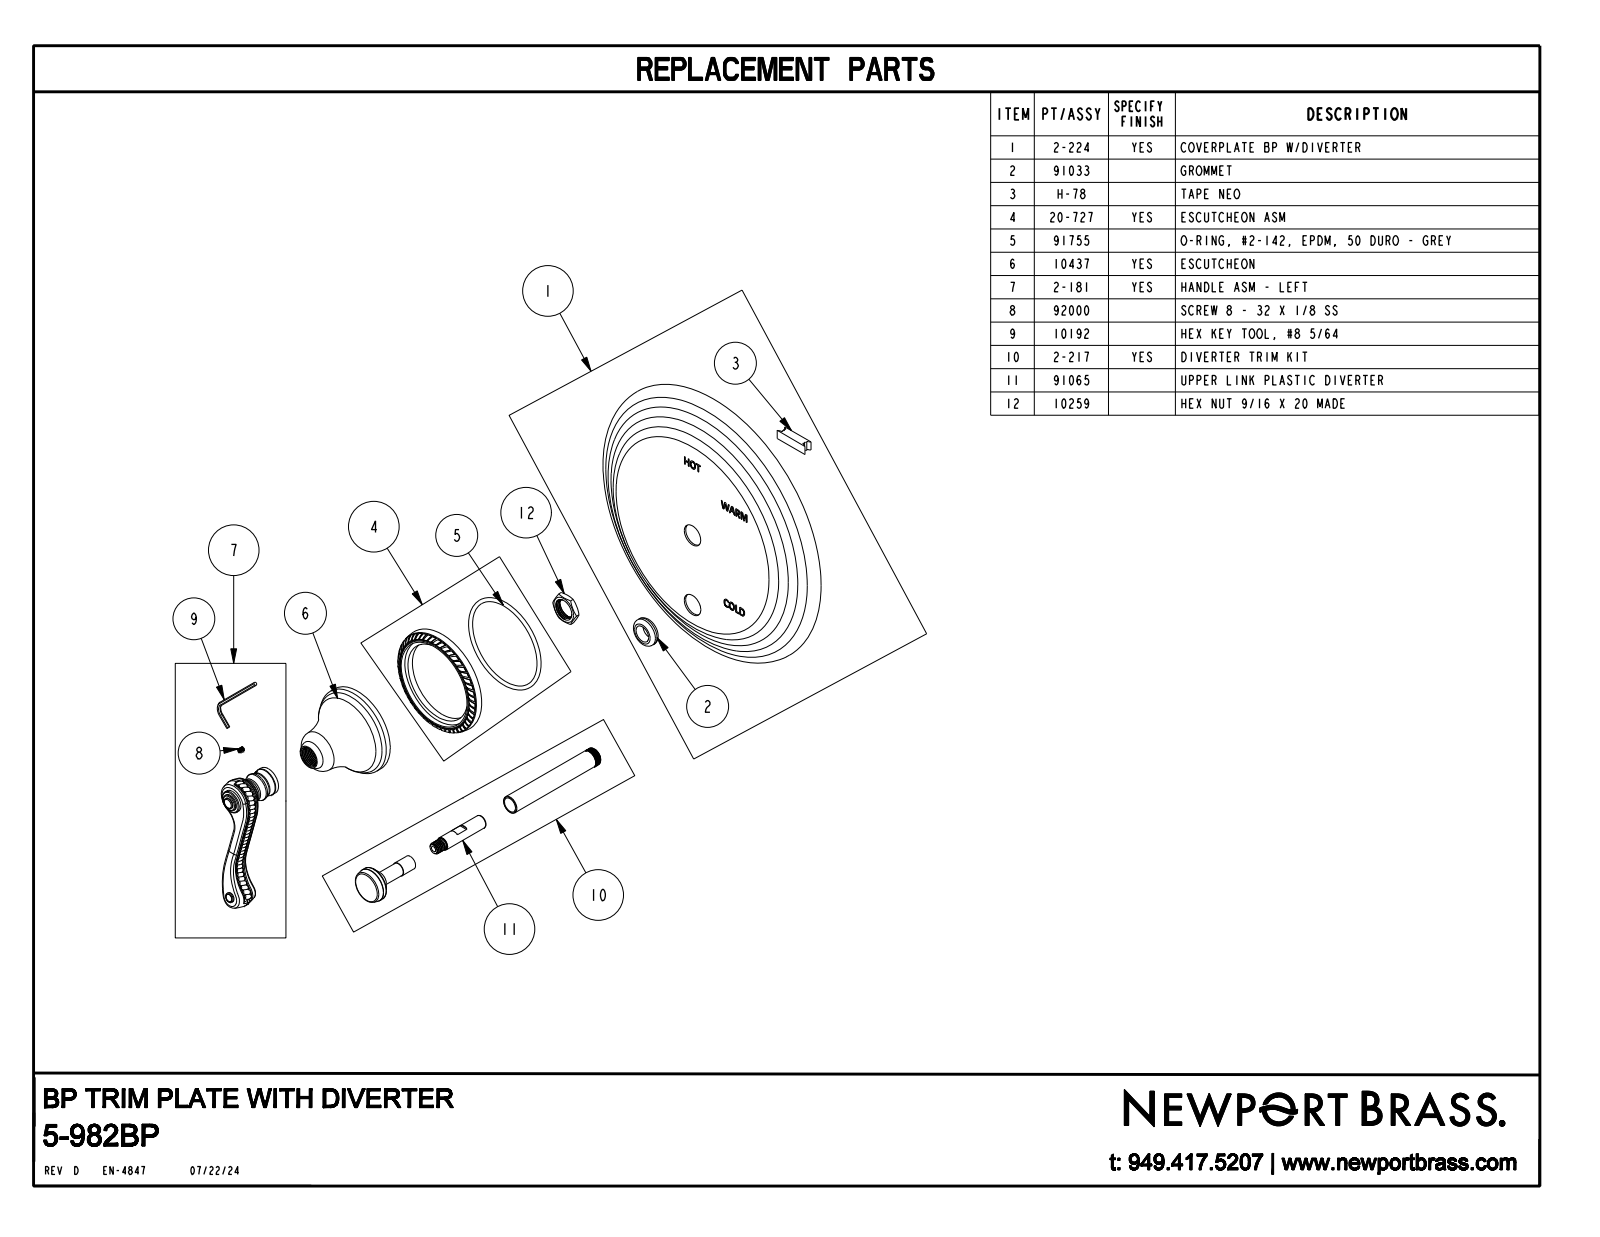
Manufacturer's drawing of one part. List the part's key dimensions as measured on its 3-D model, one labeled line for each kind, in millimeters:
Part name (STEP PRODUCT): 5-982BP
STEP written by: CREO PARAMETRIC BY PTC INC, 2018400 (CONFIG_CONTROL_DESIGN)
Units: millimetres
Bodies: 1 solid, 751 faces (215 planar, 126 cylindrical, 410 other)
Overall size (bounding box): 196.9 × 196.9 × 105.5
Volume: 556 200 mm³ · Surface area: 78 260 mm²
Round bosses / shafts (diameter × count): ⌀6.6 ×2, ⌀59.7 ×1, ⌀22.9 ×1, ⌀18.5 ×1, ⌀17.8 ×1, ⌀15.2 ×1, ⌀12 ×1, ⌀11.2 ×1
Partial cylindrical surfaces — rounded edges, fillets, slot ends (radius × count): R3.8 ×49, R2.3 ×25, R3 ×24, R279.4 ×2, R3.1 ×1, R3.5 ×1
Main face-to-face distances: 19.2, 101.2, 82, 58.1, 38.9, 43.1, 88.7, 69.6, 30.7, 12.4
